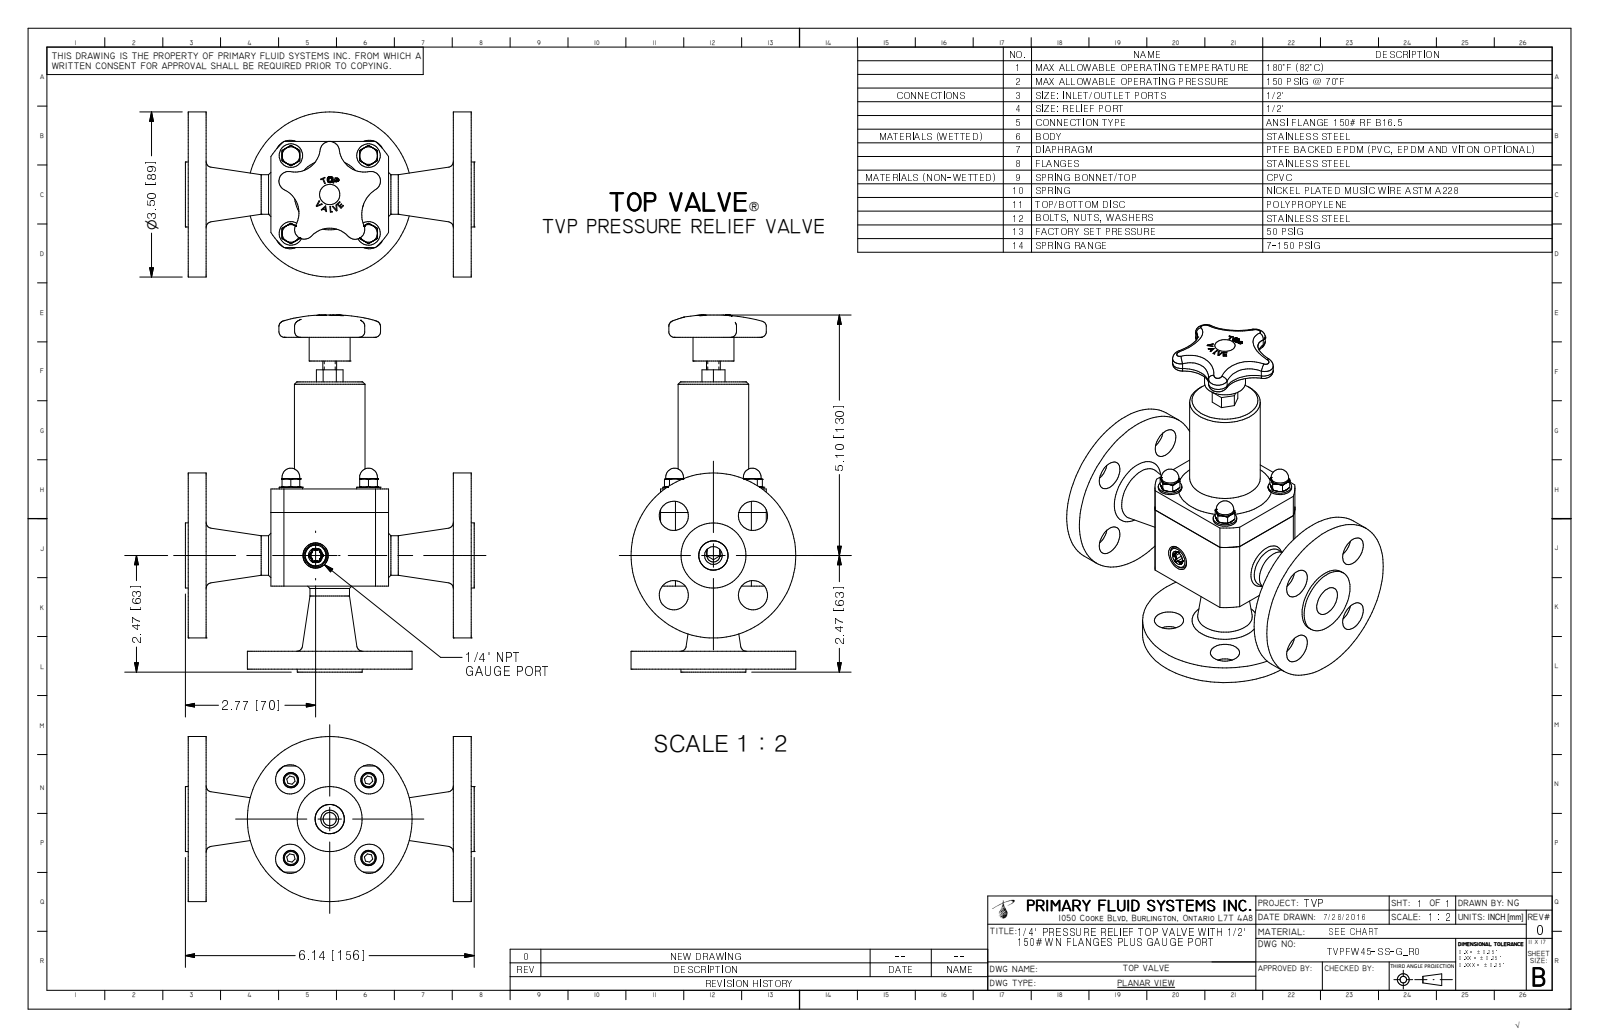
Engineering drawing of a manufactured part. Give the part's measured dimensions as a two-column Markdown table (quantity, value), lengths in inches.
| quantity | value |
| --- | --- |
| part name | TVPFW45-SS-G_R0 |
| STEP written by | Autodesk Inventor 2009 (AUTOMOTIVE_DESIGN) |
| units | inches |
| bodies | 1 solid, 414 faces (164 planar, 75 cylindrical, 175 other) |
| overall size | 7.572 × 6.14 × 3.5 |
| volume | 28.11 in³ |
| surface area | 145.2 in² |
| round holes (diameter × count) | 0.62 × 8, 0.147 × 4, 0.622 × 2, 1.525 × 1 |
| round bosses / shafts (diameter × count) | 0.5 × 4, 0.375 × 4, 0.312 × 4, 3.5 × 2, 1.38 × 2, 0.84 × 2, 1.5 × 1, 0.87 × 1 |
| partial cylindrical surfaces (radius × count) | 0.027 × 6, 0.085 × 5, 0.205 × 5, 0.536 × 4, 0.656 × 4, 0.625 × 1, 0.745 × 1, 1.488 × 1 |
| main face-to-face distances | 0.38, 5.635, 6.015, 5.255, 1.757, 4.257, 1.378, 3.878, 1.76, 1.38 |
| hole center spacings | 1.19, 1.683, 1.667, 2.357, 2.38, 0.023, 0.023, 1.167 |
